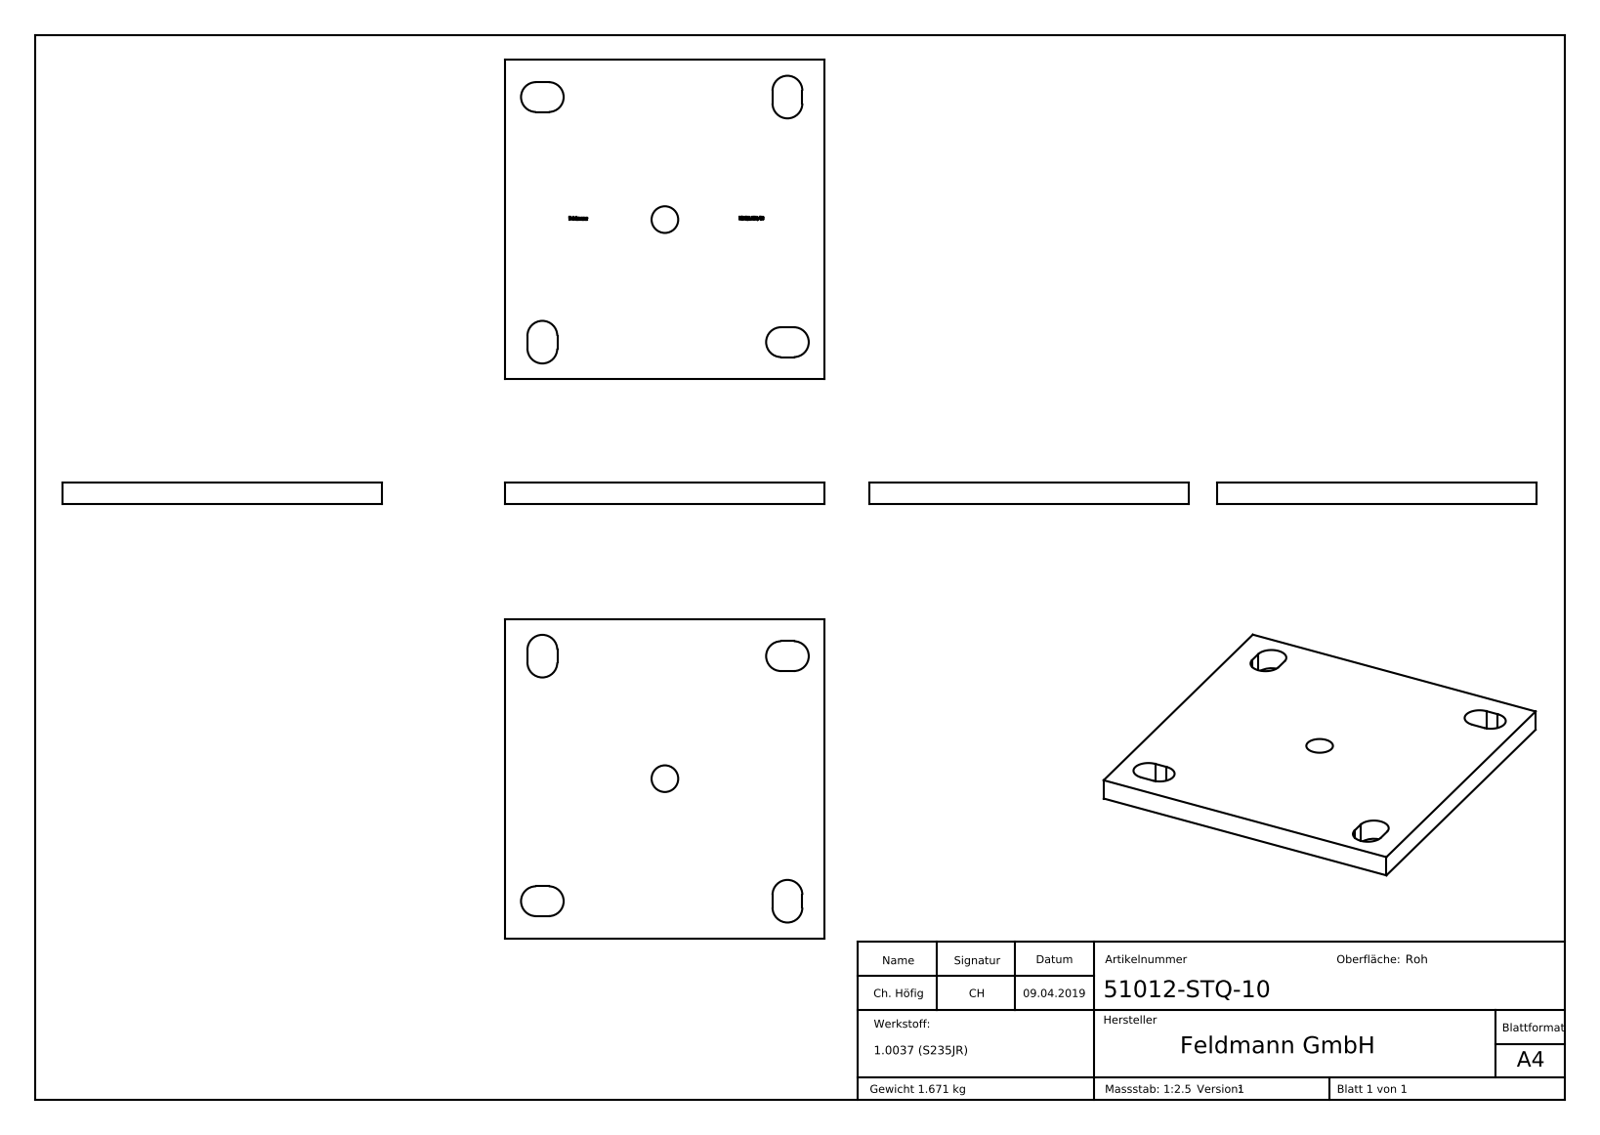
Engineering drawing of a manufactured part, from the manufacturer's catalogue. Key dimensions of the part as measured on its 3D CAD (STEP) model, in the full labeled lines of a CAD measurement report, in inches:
Part name (STEP PRODUCT): 51012-STQ-10
STEP written by: SolidWorks 2015 (CONFIG_CONTROL_DESIGN)
Units: inches
Bodies: 1 solid, 265 faces (148 planar, 12 cylindrical, 105 other)
Overall size (bounding box): 5.906 × 5.906 × 0.394
Volume: 13.07 in³ · Surface area: 79.81 in²
Round holes (diameter × count): ⌀0.492 ×1
Partial cylindrical surfaces — rounded edges, fillets, slot ends (radius × count): R0.276 ×8
Main face-to-face distances: 0.394, 5.906, 0.413, 0.965, 4.941, 5.492, 0.551, 4.528, 5.079, 3.976
